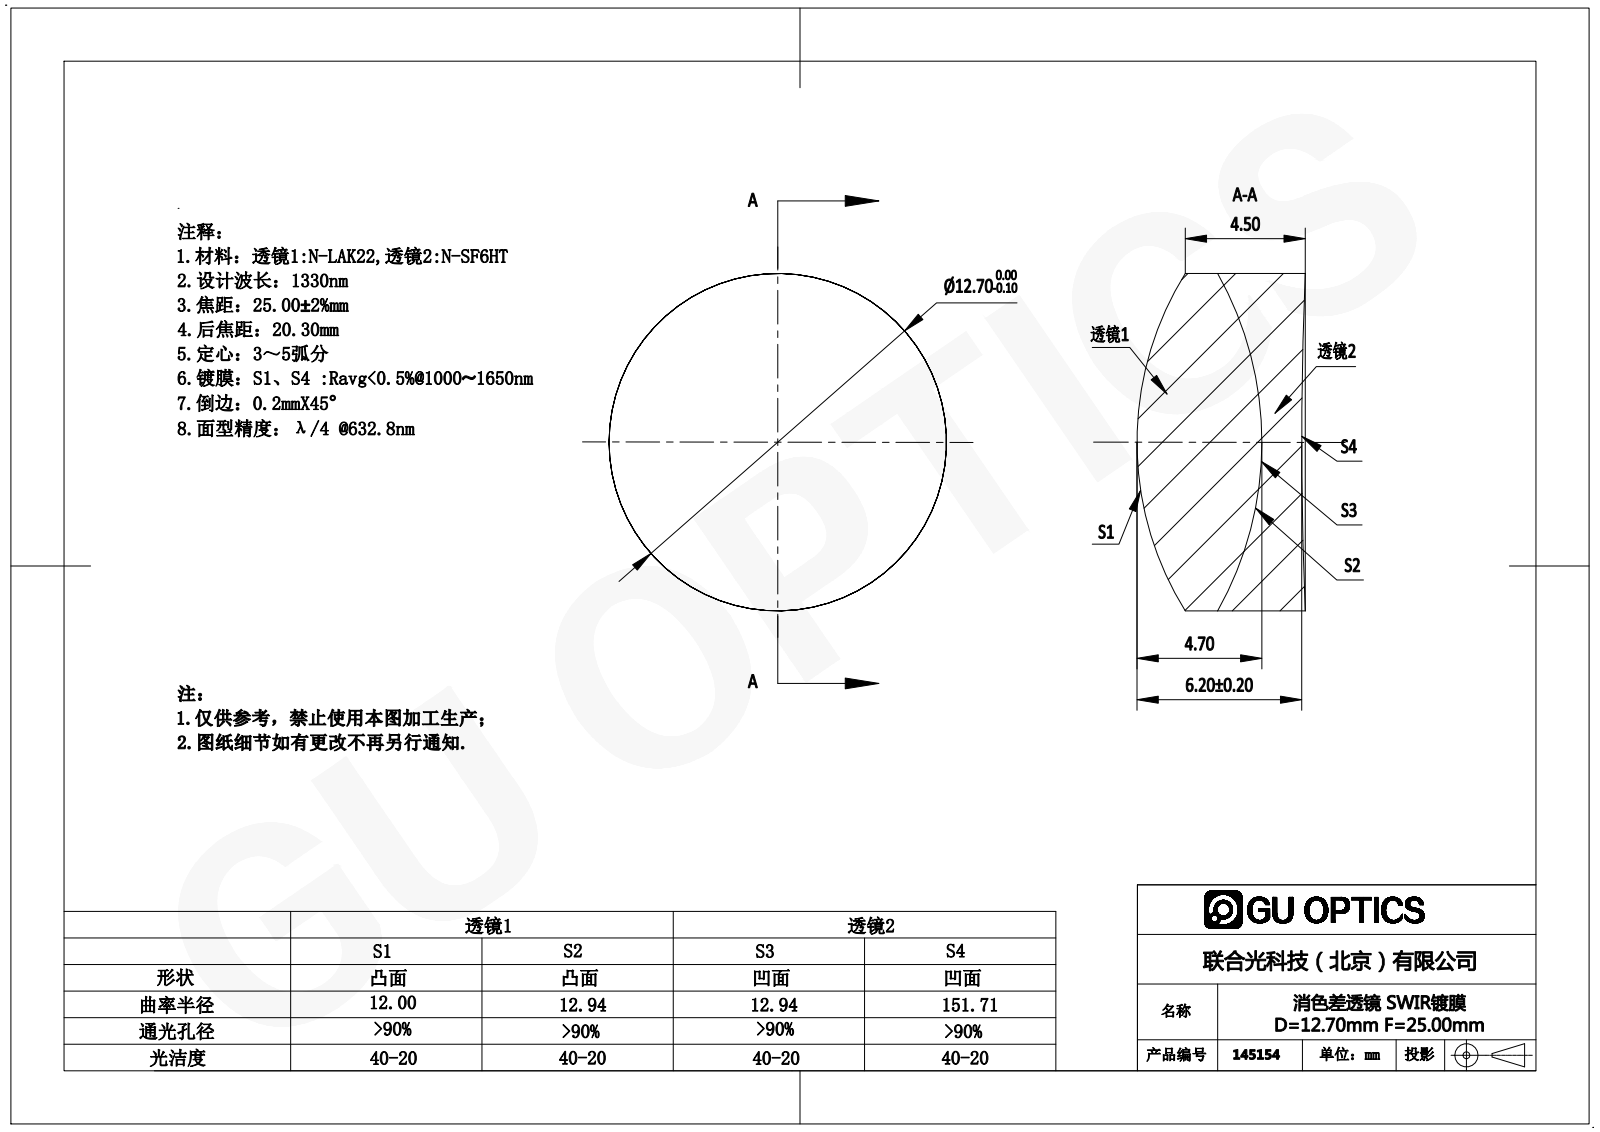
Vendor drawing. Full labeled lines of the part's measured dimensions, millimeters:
Part name (STEP PRODUCT): 145154
STEP written by: SolidWorks 2016 (AUTOMOTIVE_DESIGN)
Units: millimetres
Bodies: 2 solids, 12 faces (0 planar, 4 cylindrical, 8 other)
Overall size (bounding box): 12.7 × 12.7 × 6.33
Volume: 682 mm³ · Surface area: 715 mm²
Round bosses / shafts (diameter × count): ⌀12.7 ×1
